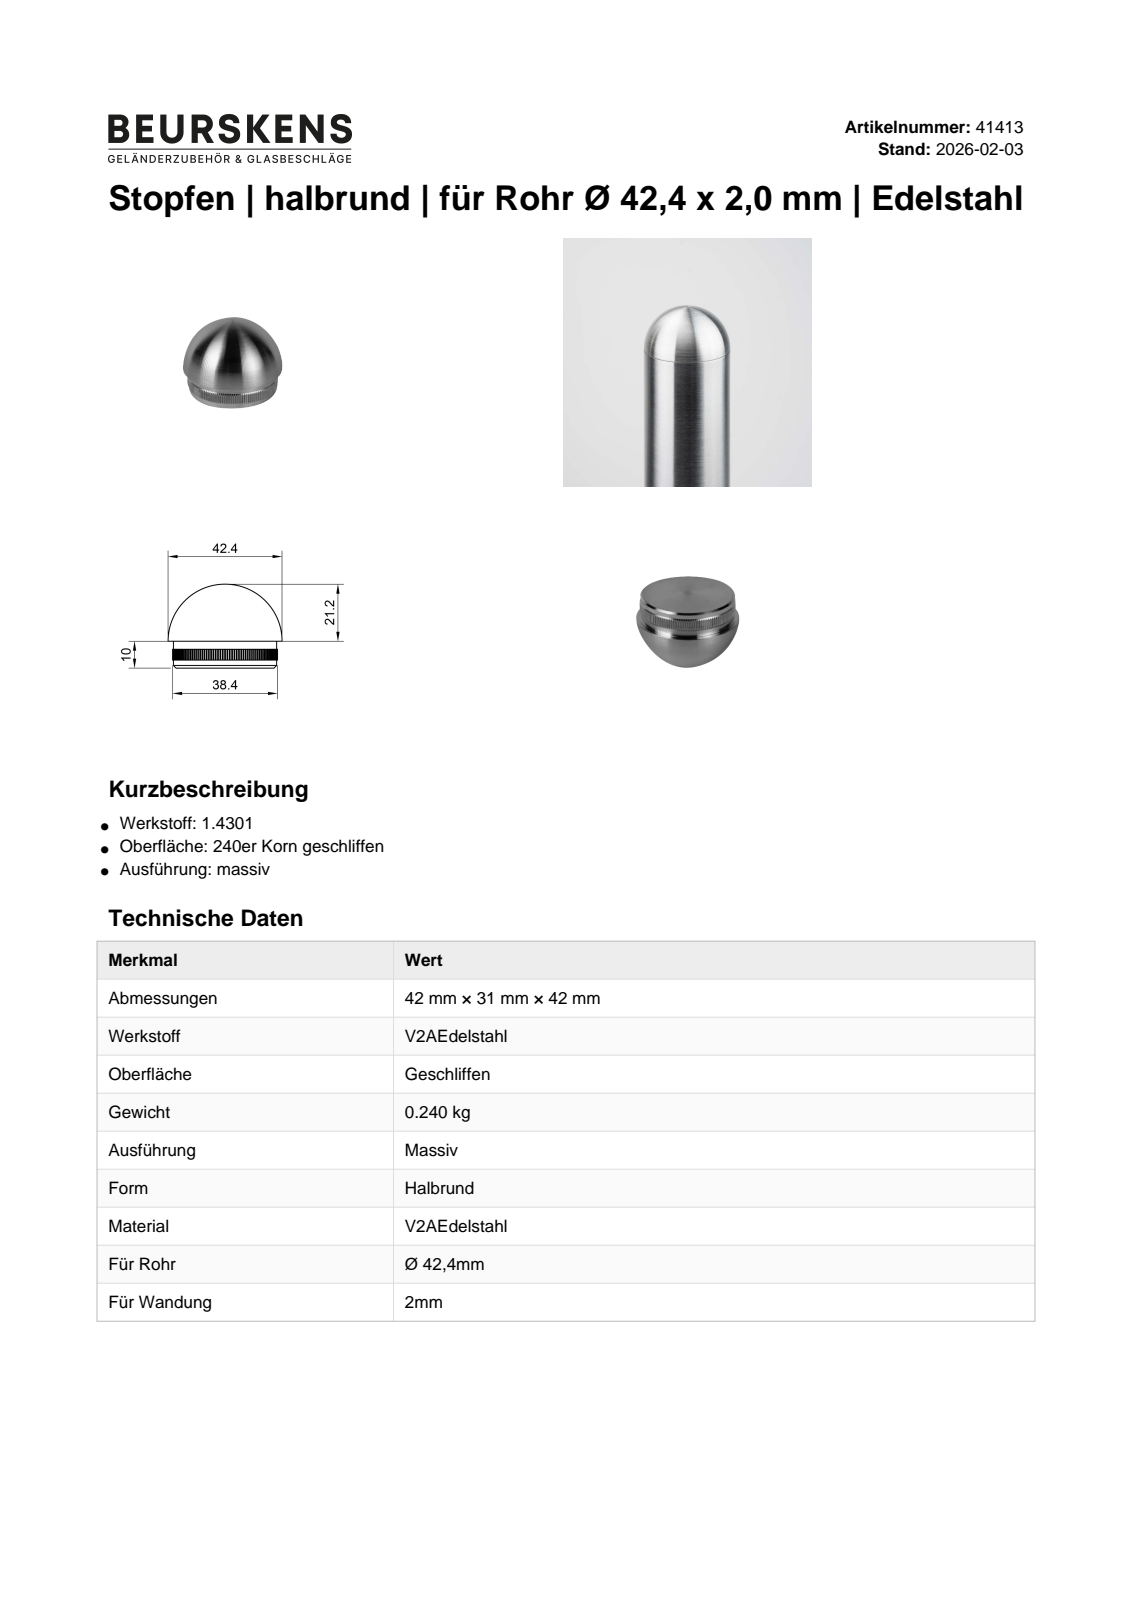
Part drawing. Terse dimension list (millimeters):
name: 41413
written by: Autodesk Inventor 2022 (AUTOMOTIVE_DESIGN)
unit: mm
bodies: 1 solid, 288 faces (4 planar, 282 cylindrical, 2 other)
size: 42.4 × 42.4 × 31.2
volume: 31 610 mm³; area: 5 523 mm²
bosses: 1× ⌀38.4
rounds: 140× R0.12, 1× R19.5
face distances: 10, 3, 7, 4
